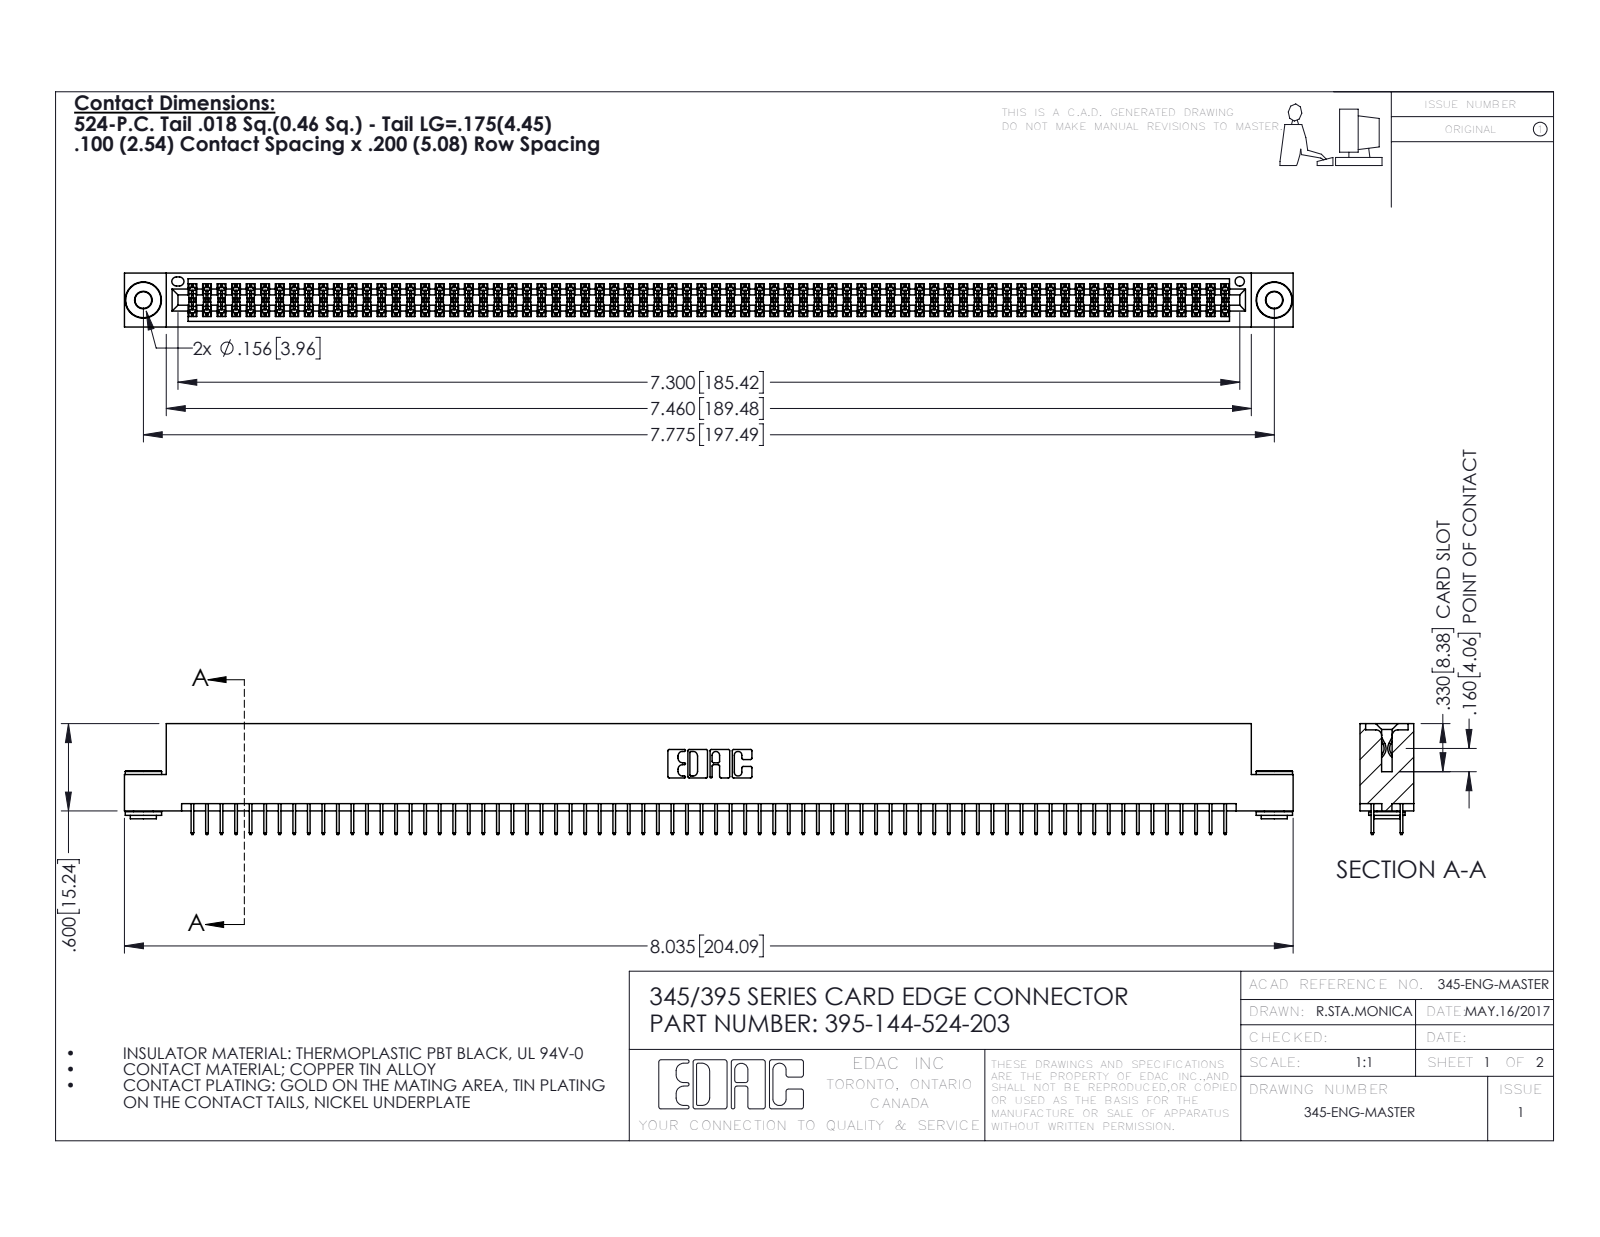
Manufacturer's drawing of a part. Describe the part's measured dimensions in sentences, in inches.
The part is named "395-144-524-203; 345 Part_Flush Mounting Lugs - 0.156 Dia-TH; 345-250-002_345-250-002-102; 345-292-001_345-293-124". Its 3-D file was written by "SolidWorks 2016 (CONFIG_CONTROL_DESIGN)". It is 147 solids with 7940 faces: 5706 planar, 2226 cylindrical and 8 other. Overall it measures 8.035 by 0.762 by 0.37 inches. Its volume is 1.215 cubic inches and its surface area 45.93 square inches. Round holes: 2 of diameter 0.116, 2 of diameter 0.156, 1 of diameter 0.064. Round bosses or shafts: 2 of diameter 0.25, 2 of diameter 0.18, 2 of diameter 0.136. Partial cylindrical surfaces (rounded edges, fillets, slot ends): 216 of radius 0.006, 22 of radius 0.01, 6 of radius 0.007, 6 of radius 0.031, 3 of radius 0.026, 2 of radius 0.014, 2 of radius 0.019, 2 of radius 0.022. The main face-to-face distances are 0.072, 0.298, 0.2, 0.37, 0.025, 0.098, 0.272, 0.225, 0.072, 0.175. The hole center spacings are 0.27, 7.539, 7.775.
